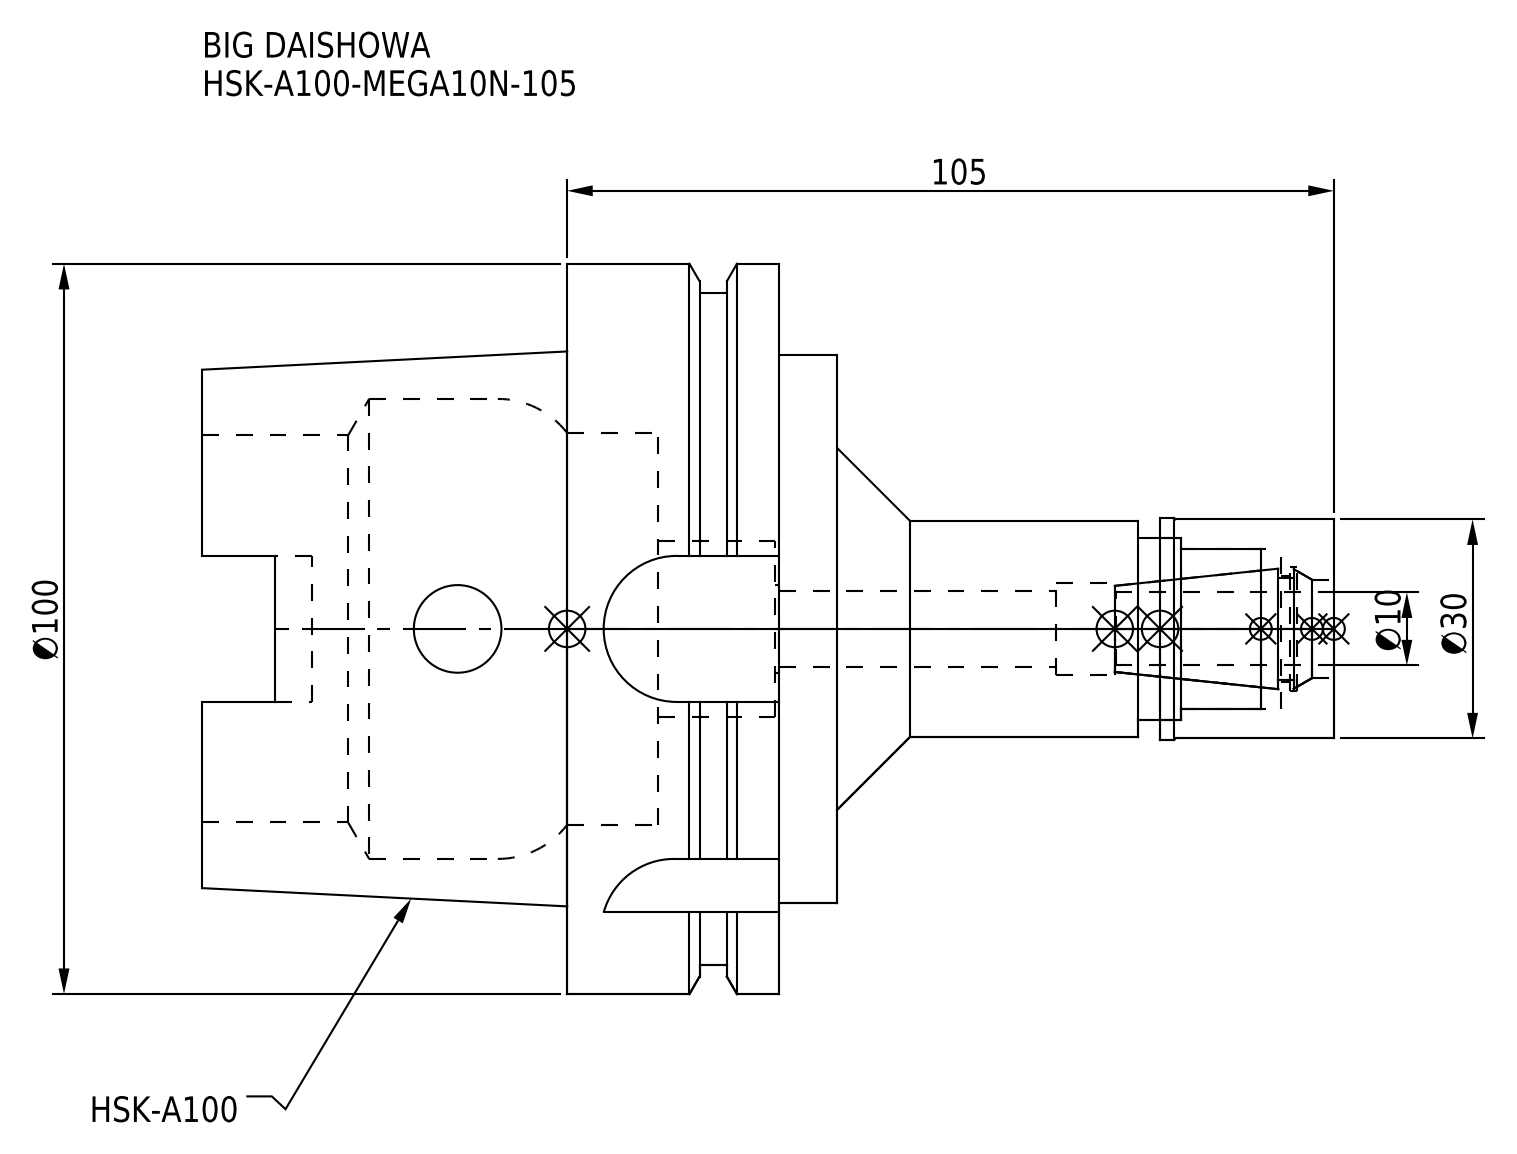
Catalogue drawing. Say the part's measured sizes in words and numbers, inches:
The part is named "HSK-A100-MEGA10N-105-100-FreeParts; HSK-A100-MEGA10N-105_1.stp; HA100MN10105-100_ASM.stp; HSK-A100-MEGA10N-105 (+3 more)". Its 3-D file was written by "SolidWorks 2019 (CONFIG_CONTROL_DESIGN)". It is 2 solids with 124 faces: 44 planar, 58 cylindrical and 22 other. Overall it measures 6.102 by 3.937 by 3.937 inches. Its volume is 20.23 cubic inches and its surface area 98.74 square inches. Round holes: 2 of diameter 0.472, 1 of diameter 0.409, 1 of diameter 0.492, 1 of diameter 0.531, 1 of diameter 0.571, 1 of diameter 0.669, 1 of diameter 0.866, 1 of diameter 0.945, 1 of diameter 0.984, 1 of diameter 2.087, 1 of diameter 2.118, 1 of diameter 2.48. Round bosses or shafts: 1 of diameter 3.937, 1 of diameter 3.622, 1 of diameter 2.953, 1 of diameter 1.193, 1 of diameter 1.181, 1 of diameter 1.161. Partial cylindrical surfaces (rounded edges, fillets, slot ends): 4 of radius 0.192, 4 of radius 0.394. The main face-to-face distances are 1.142, 0.315, 1.457, 0.967, 0.652, 0.49, 3.425, 3.11, 2.459, 1.969.
